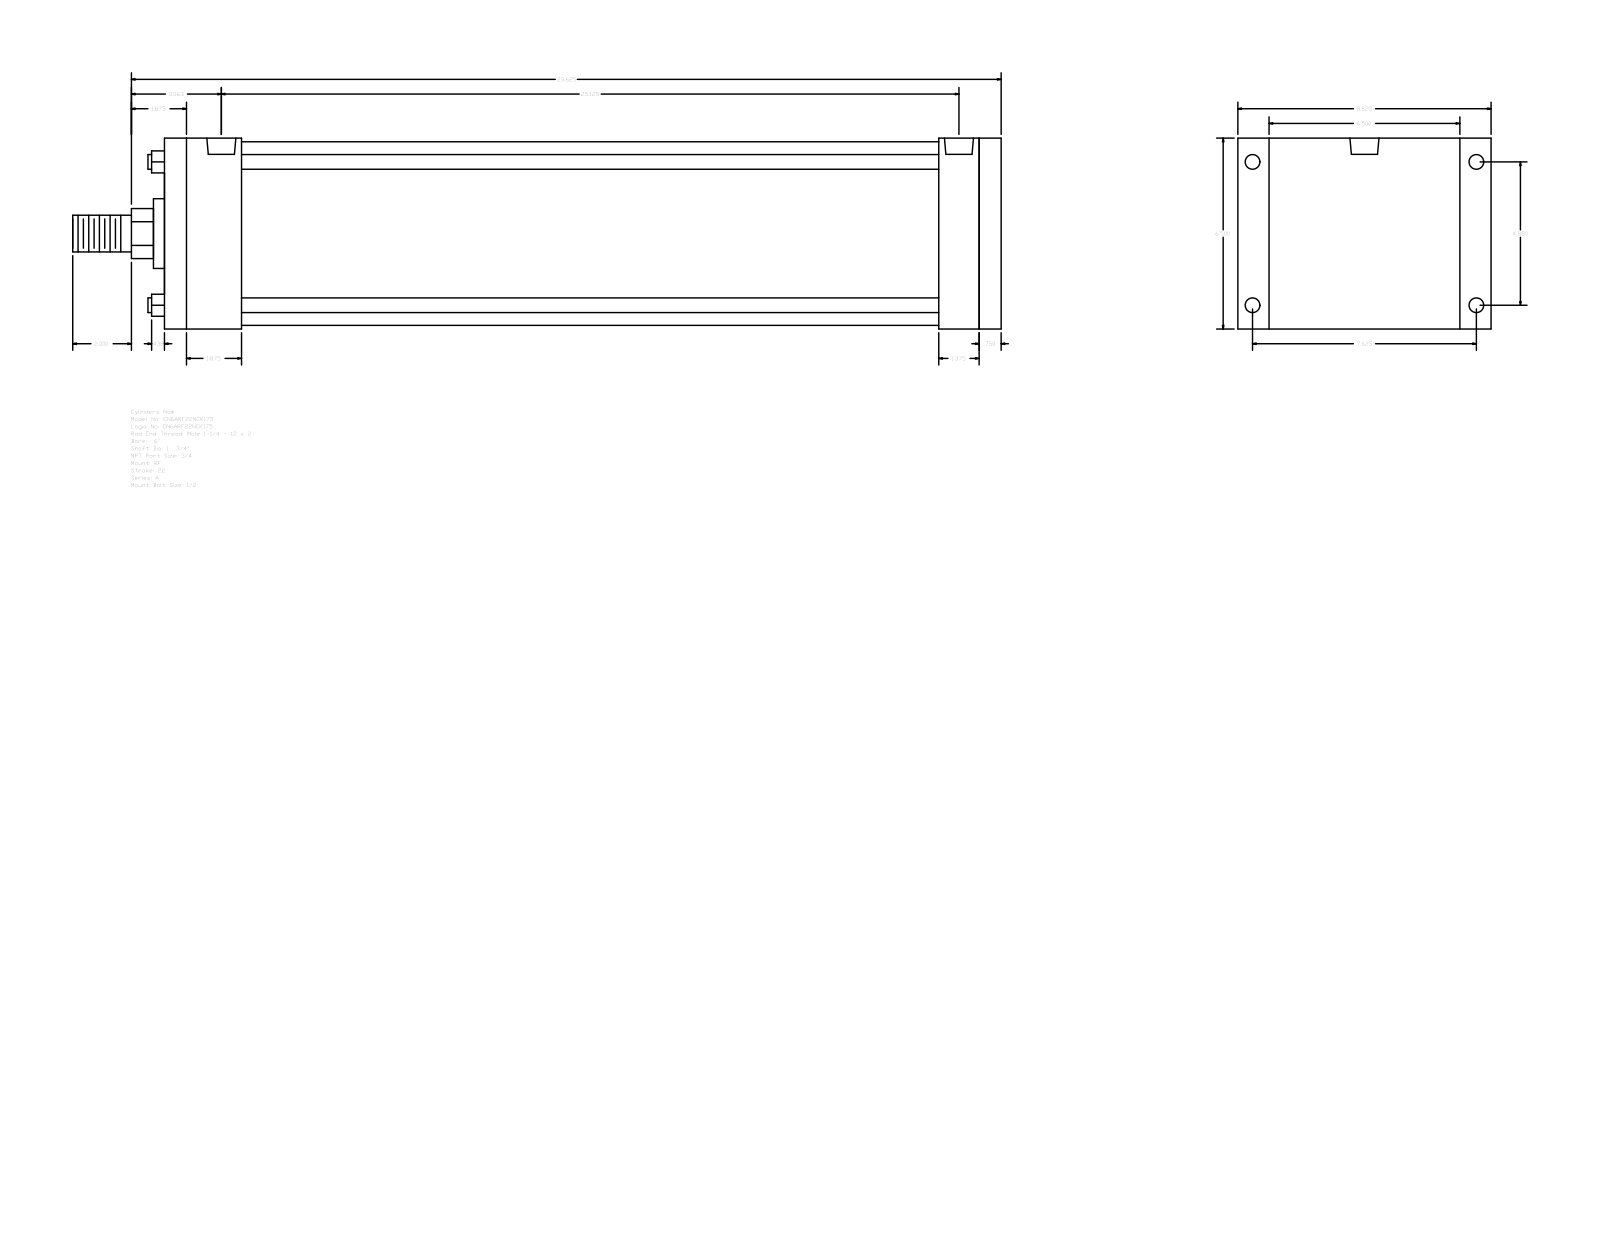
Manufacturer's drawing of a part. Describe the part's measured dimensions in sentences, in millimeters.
The part is named "A_RF__0600_1.75". Its 3-D file was written by "GSSL Pune (CONFIG_CONTROL_DESIGN)". It is 0 solids with 92 faces: 64 planar, 28 cylindrical and 0 other. Overall it measures 803.27 by 219.07 by 165.1 millimeters. Round holes: 4 of diameter 12.7, 4 of diameter 15.08, 2 of diameter 25.12. Round bosses or shafts: 4 of diameter 12.7, 1 of diameter 158.75, 1 of diameter 60.33, 1 of diameter 44.45, 1 of diameter 31.75. Partial cylindrical surfaces (rounded edges, fillets, slot ends): 1 of radius 21.63. The main face-to-face distances are 165.1, 723.91, 704.85, 19.06, 66.68, 638.17, 657.23, 669.93, 603.25, 34.92. The hole center spacings are 5.56, 123.96, 193.68, 229.95, 627.05, 632.61, 638.17.
